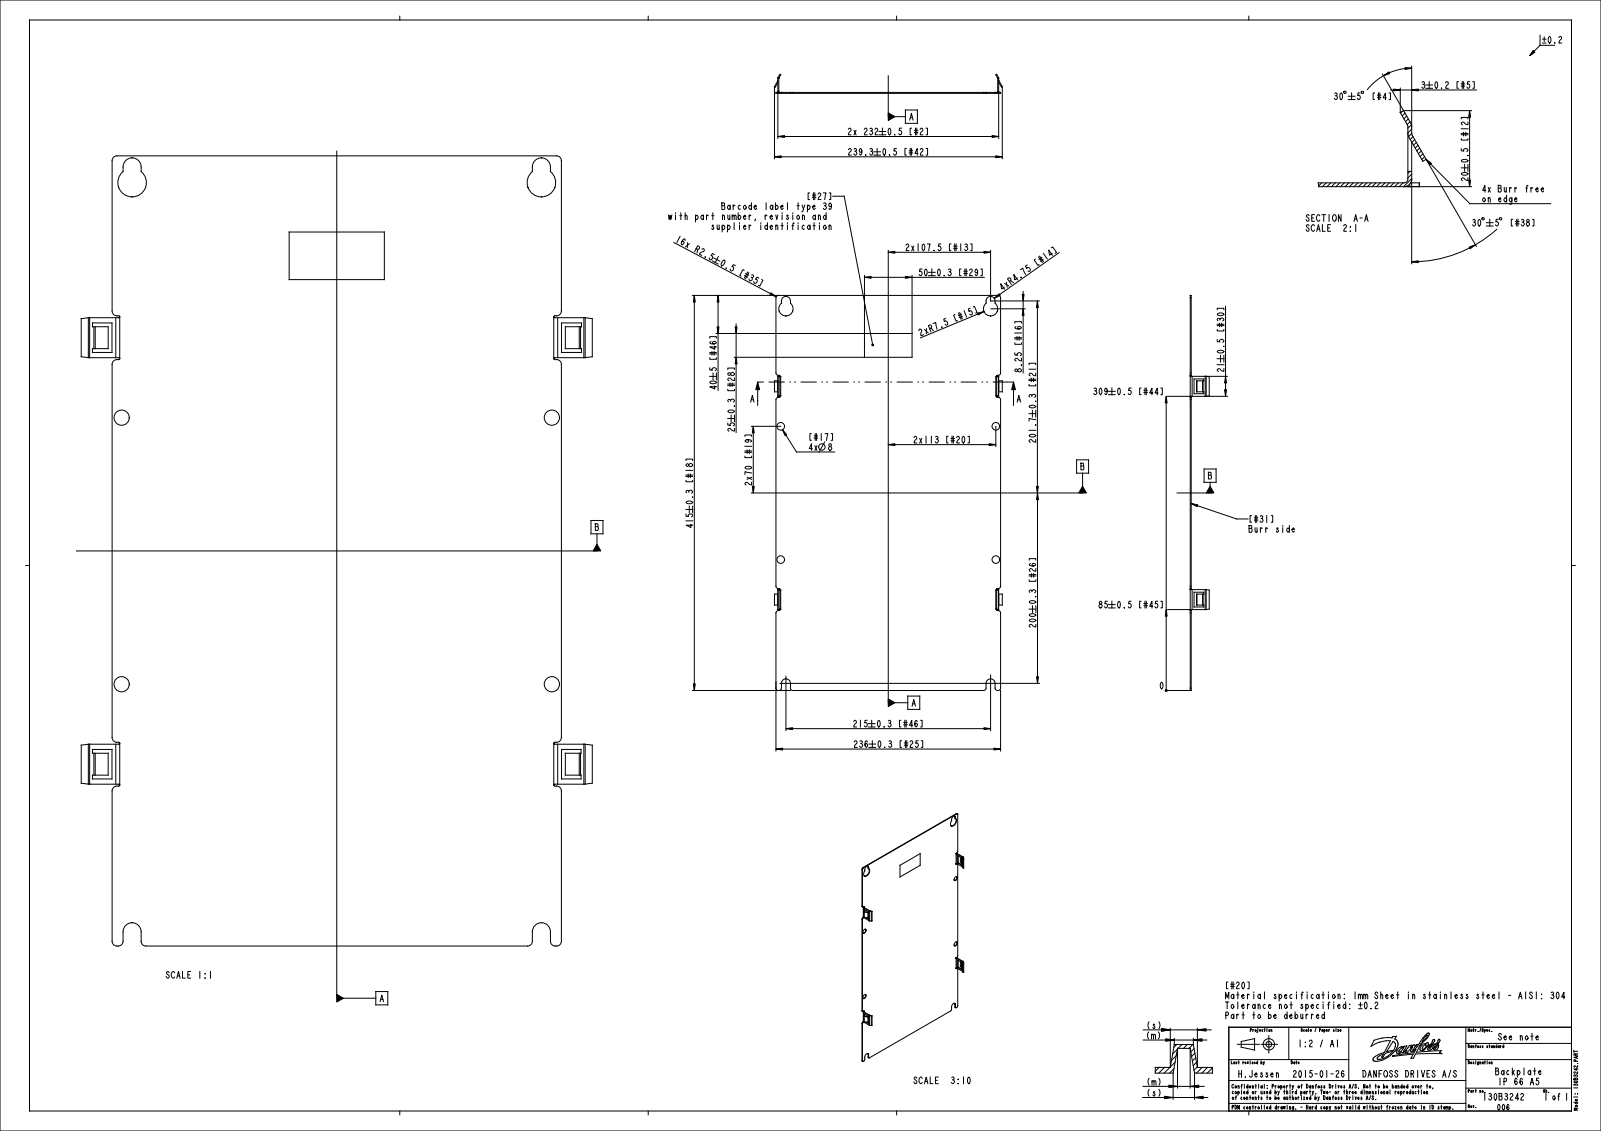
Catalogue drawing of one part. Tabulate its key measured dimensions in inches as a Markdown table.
| quantity | value |
| --- | --- |
| part name | 130B3242 |
| STEP written by | CREO PARAMETRIC BY PTC INC, 2018070 (CONFIG_CONTROL_DESIGN) |
| units | inches |
| bodies | 1 solid, 214 faces (136 planar, 62 cylindrical, 16 other) |
| overall size | 16.339 × 9.422 × 0.786 |
| volume | 5.99 in³ |
| surface area | 307.4 in² |
| round holes (diameter × count) | 0.315 × 4 |
| partial cylindrical surfaces (radius × count) | 0.098 × 16, 0.02 × 8, 0.039 × 6, 0.079 × 6, 0.187 × 4, 0.295 × 2 |
| main face-to-face distances | 0.039, 0.079, 0.118, 9.213, 9.173, 9.094, 9.291, 0.05, 0.06, 9.134 |
| hole center spacings | 5.512, 8.898, 10.467 |
